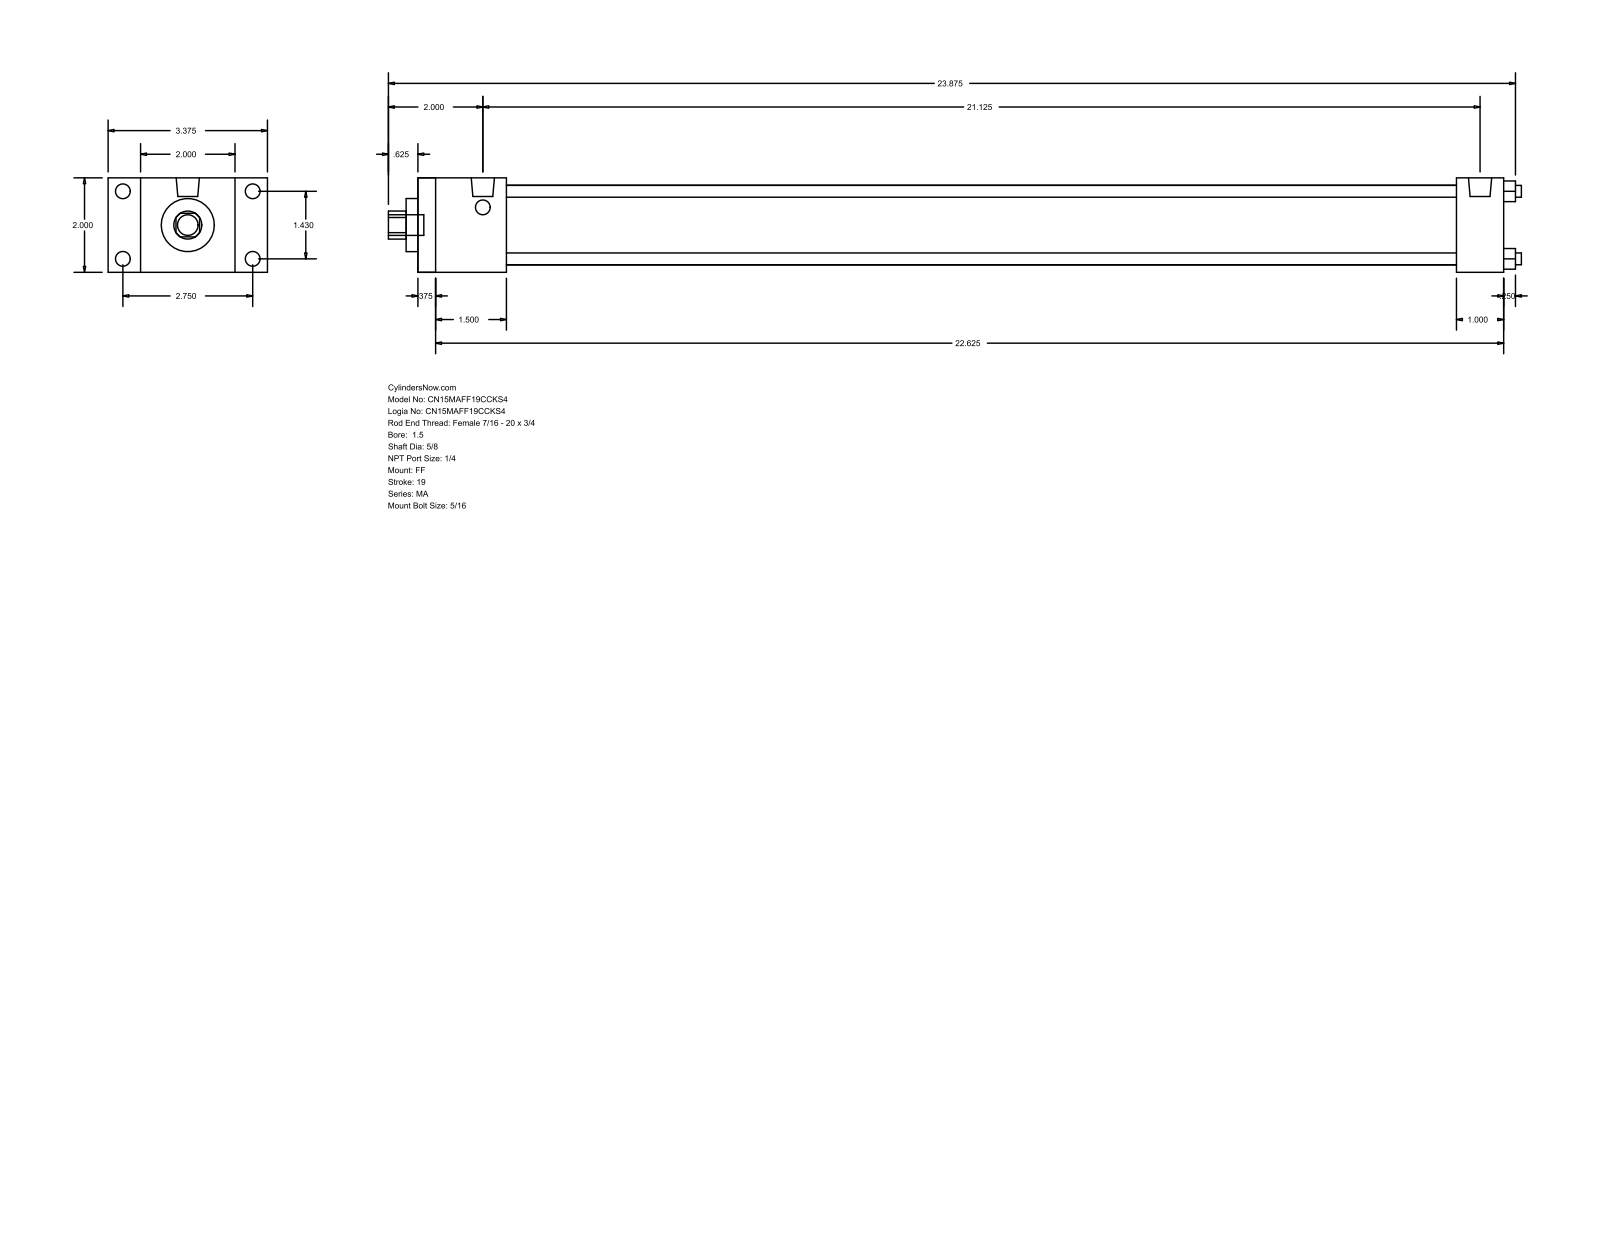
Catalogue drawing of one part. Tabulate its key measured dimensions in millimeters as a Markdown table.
| quantity | value |
| --- | --- |
| part name | MA_FF__0150_0.625 |
| STEP written by | GSSL Pune (CONFIG_CONTROL_DESIGN) |
| units | millimeters |
| bodies | 0 solids, 92 faces (64 planar, 28 cylindrical, 0 other) |
| overall size | 609.6 × 85.72 × 50.8 |
| round holes (diameter × count) | 6.35 × 4, 15.88 × 1, 28.57 × 1, 42.93 × 1 |
| round bosses / shafts (diameter × count) | 7.94 × 8, 12.49 × 2, 11.11 × 1 |
| partial cylindrical surfaces (radius × count) | 7.54 × 1 |
| main face-to-face distances | 50.8, 584.2, 9.52, 574.68, 47.62, 558.79, 38.1, 549.27, 511.17, 536.58 |
| hole center spacings | 25.68, 36.32, 51.36 |
